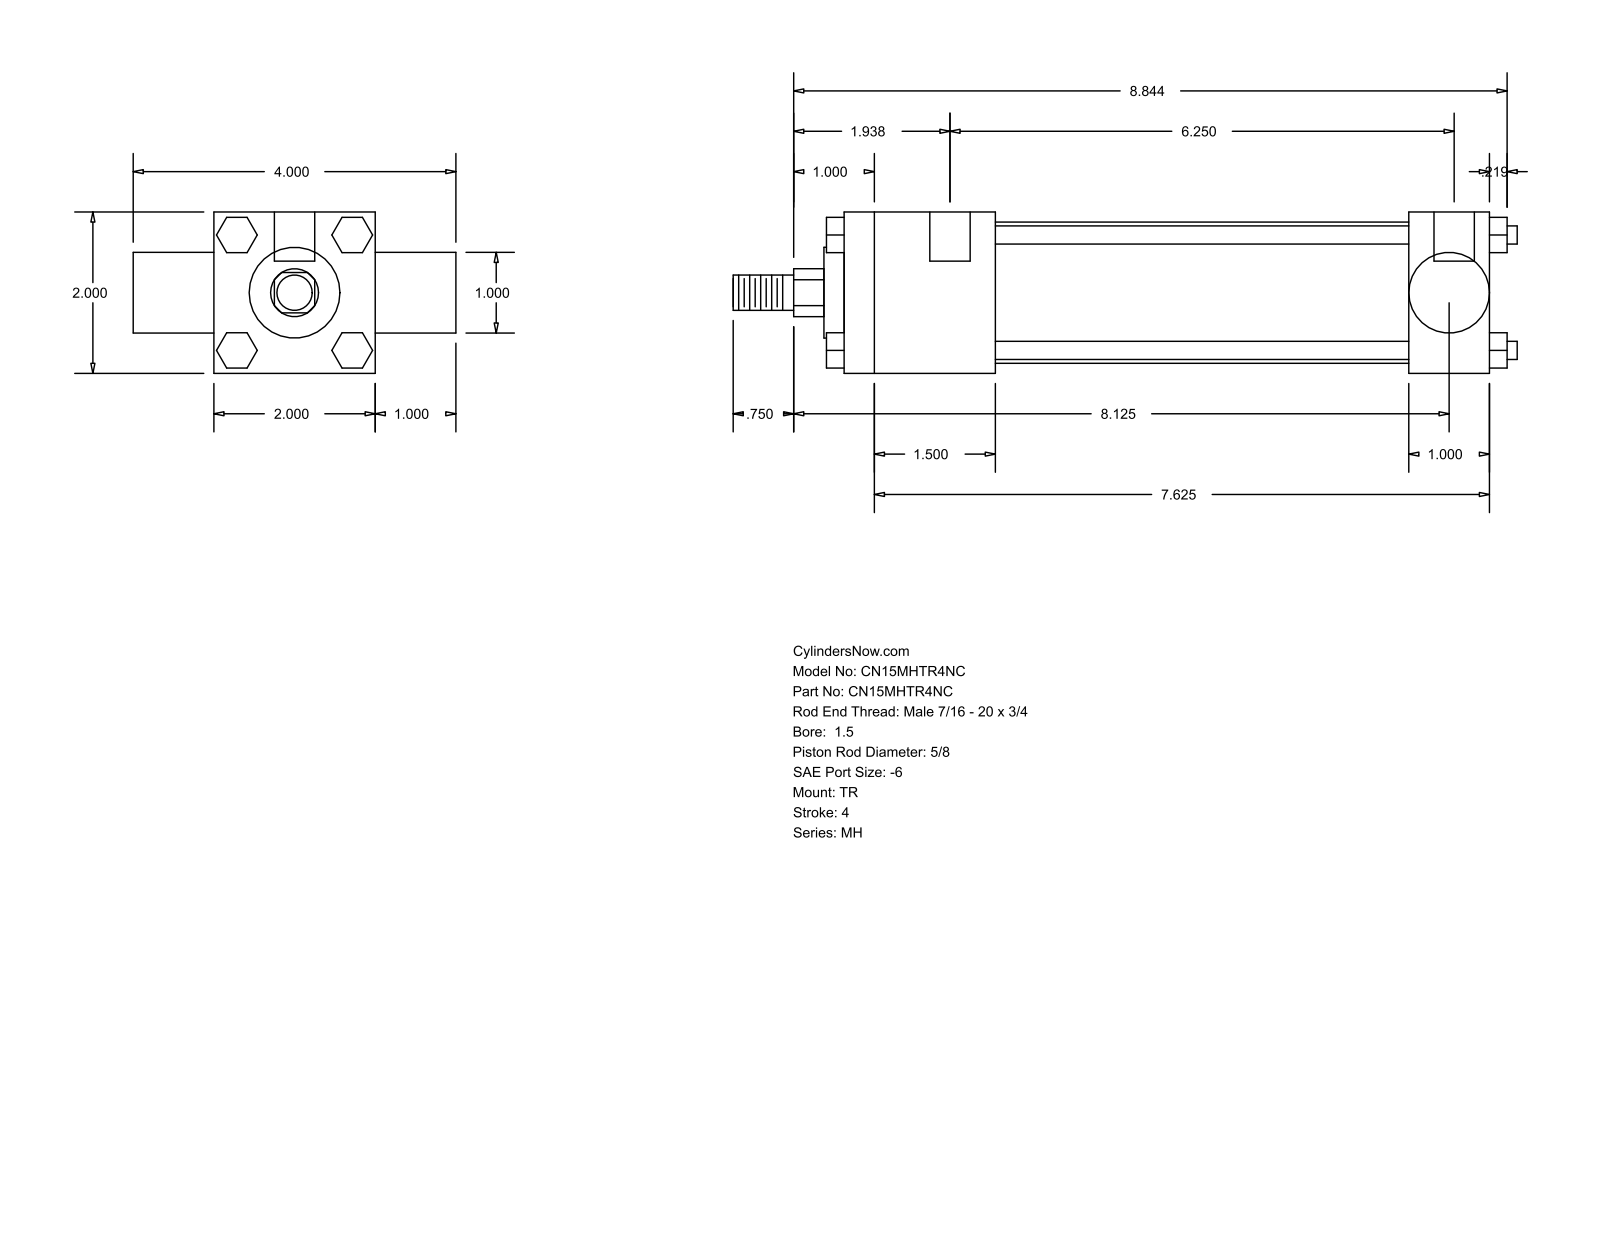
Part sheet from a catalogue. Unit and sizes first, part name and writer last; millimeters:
Units: millimetres
Overall size (bounding box): 246.86 × 101.6 × 50.8
Round holes (diameter × count): ⌀5.56 ×3, ⌀12.7 ×2
Round bosses / shafts (diameter × count): ⌀5.71 ×4, ⌀44.45 ×1, ⌀28.57 ×1, ⌀25.35 ×1, ⌀15.88 ×1, ⌀11.11 ×1
Partial cylindrical surfaces — rounded edges, fillets, slot ends (radius × count): R7.54 ×1
Main face-to-face distances: 50.8, 203.19, 25.4, 76.2, 47.62, 155.57, 177.8, 130.18, 25.39, 5.56
Hole centre spacings: 3.17, 158.75, 161.92
Bodies: 0 solids, 120 faces (92 planar, 28 cylindrical, 0 other)
Part name (STEP PRODUCT): MH_TR__0150_0.625
STEP written by: GSSL Pune (CONFIG_CONTROL_DESIGN)
